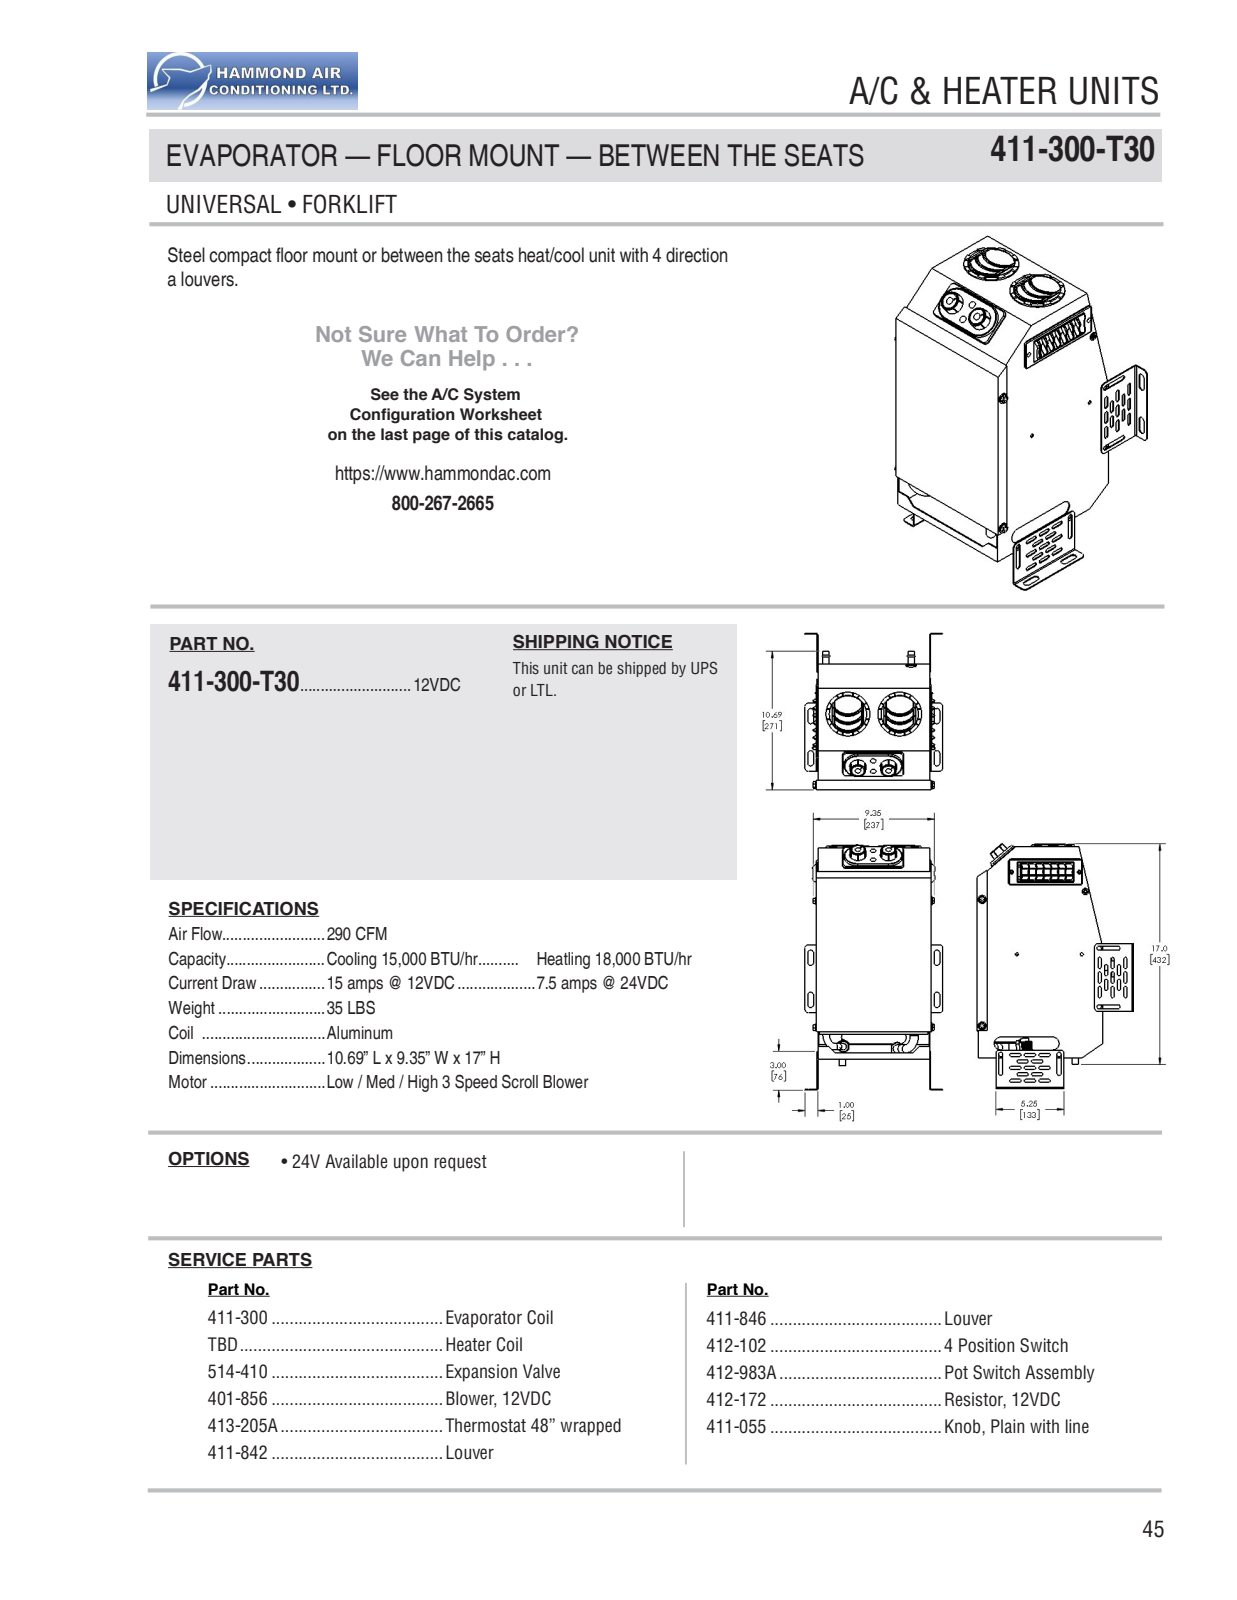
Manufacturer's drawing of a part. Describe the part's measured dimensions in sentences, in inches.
The part is named "520-HAC-001; 520-T30-11; teste; GLO-PARV-S001-00 (+8 more)". Its 3-D file was written by "SolidWorks 2022 (CONFIG_CONTROL_DESIGN)". It is 97 solids with 7494 faces: 3256 planar, 2256 cylindrical and 1982 other. Overall it measures 18.524 by 12.939 by 12.937 inches. Its volume is 409.5 cubic inches and its surface area 3 348 square inches. Round holes: 15 of diameter 0.096, 13 of diameter 0.391, 12 of diameter 0.205, 8 of diameter 0.313, 6 of diameter 0.093, 4 of diameter 0.079, 4 of diameter 0.106, 4 of diameter 0.156, 4 of diameter 0.475, 3 of diameter 0.281, 3 of diameter 0.5, 2 of diameter 0.195. Round bosses or shafts: 27 of diameter 0.375, 15 of diameter 0.116, 15 of diameter 0.062, 12 of diameter 0.125, 10 of diameter 0.5, 7 of diameter 0.375, 6 of diameter 0.625, 4 of diameter 0.625. Partial cylindrical surfaces (rounded edges, fillets, slot ends): 151 of radius 0.02, 120 of radius 0.125, 52 of radius 0.039, 48 of radius 0.007, 46 of radius 0.375, 40 of radius 0.03, 34 of radius 0.156, 28 of radius 0.059. The main face-to-face distances are 0.063, 0.062, 8.625, 8.5, 8.563, 8.562, 7.253, 7.375, 0.105, 10.441. The hole center spacings are 0.559, 0.25, 0.354, 0.5, 2.362, 0.274, 0.791, 0.5.
